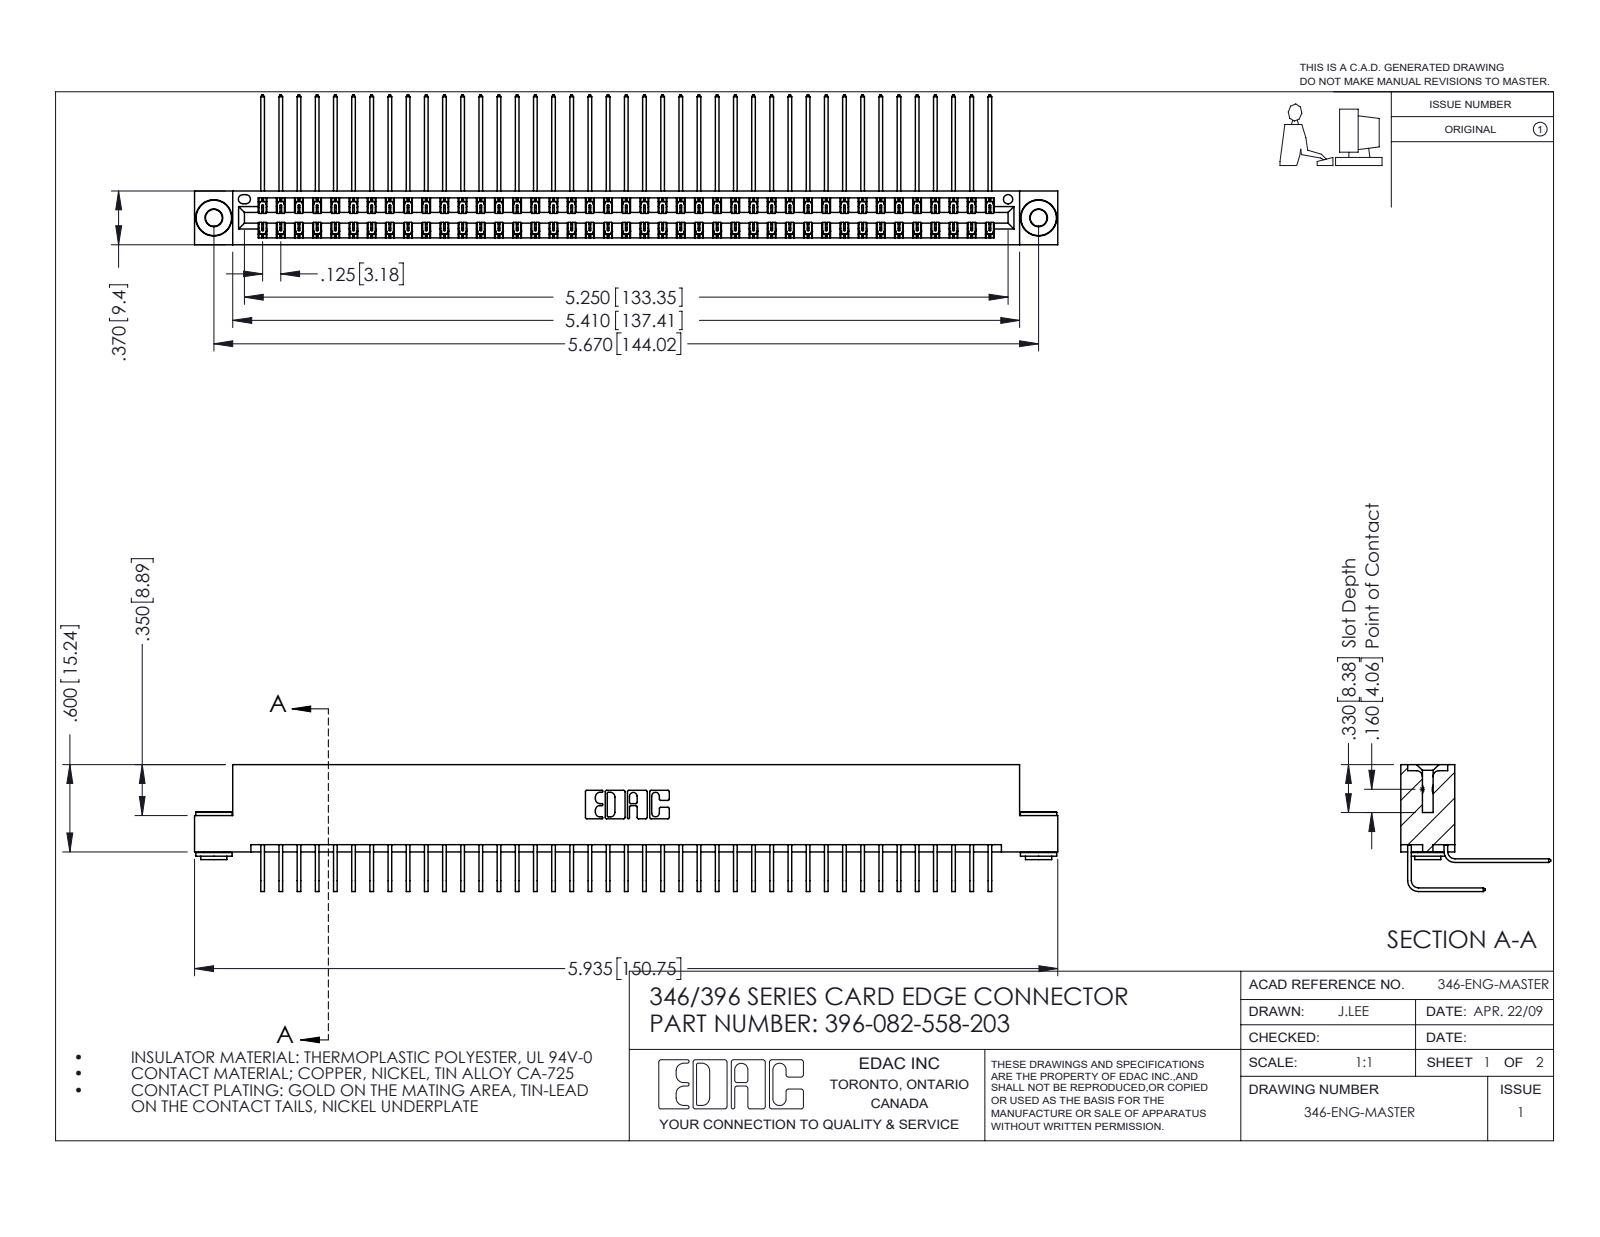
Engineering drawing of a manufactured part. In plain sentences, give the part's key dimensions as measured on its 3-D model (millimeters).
The part is named "346 Part_Flush Mounting Lugs - 0.156 Dia-TH; 396-082-558-203; 345-292-001_558 Tail - 2; 345-250-002_345-250-002-102 (+1 more)". Its 3-D file was written by "SolidWorks 2016 (CONFIG_CONTROL_DESIGN)". It is 85 solids with 4588 faces: 3120 planar, 1460 cylindrical and 8 other. Overall it measures 150.7 by 26.2 by 22.2 millimeters. Its volume is 15 200 cubic millimeters and its surface area 23 340 square millimeters. Round holes: 2 of diameter 2.9, 2 of diameter 4, 1 of diameter 1.6. Round bosses or shafts: 2 of diameter 6.4, 2 of diameter 4.6, 2 of diameter 3.5. Partial cylindrical surfaces (rounded edges, fillets, slot ends): 123 of radius 0.2, 22 of radius 0.3, 6 of radius 0.2, 6 of radius 0.8, 3 of radius 0.7, 2 of radius 0.4, 2 of radius 0.6, 2 of radius 0.6. The main face-to-face distances are 8.2, 1.2, 0.6, 6.4, 9.4, 7.6, 1.8, 7, 3.8, 5.6. The hole center spacings are 6.2, 138.7, 144.
